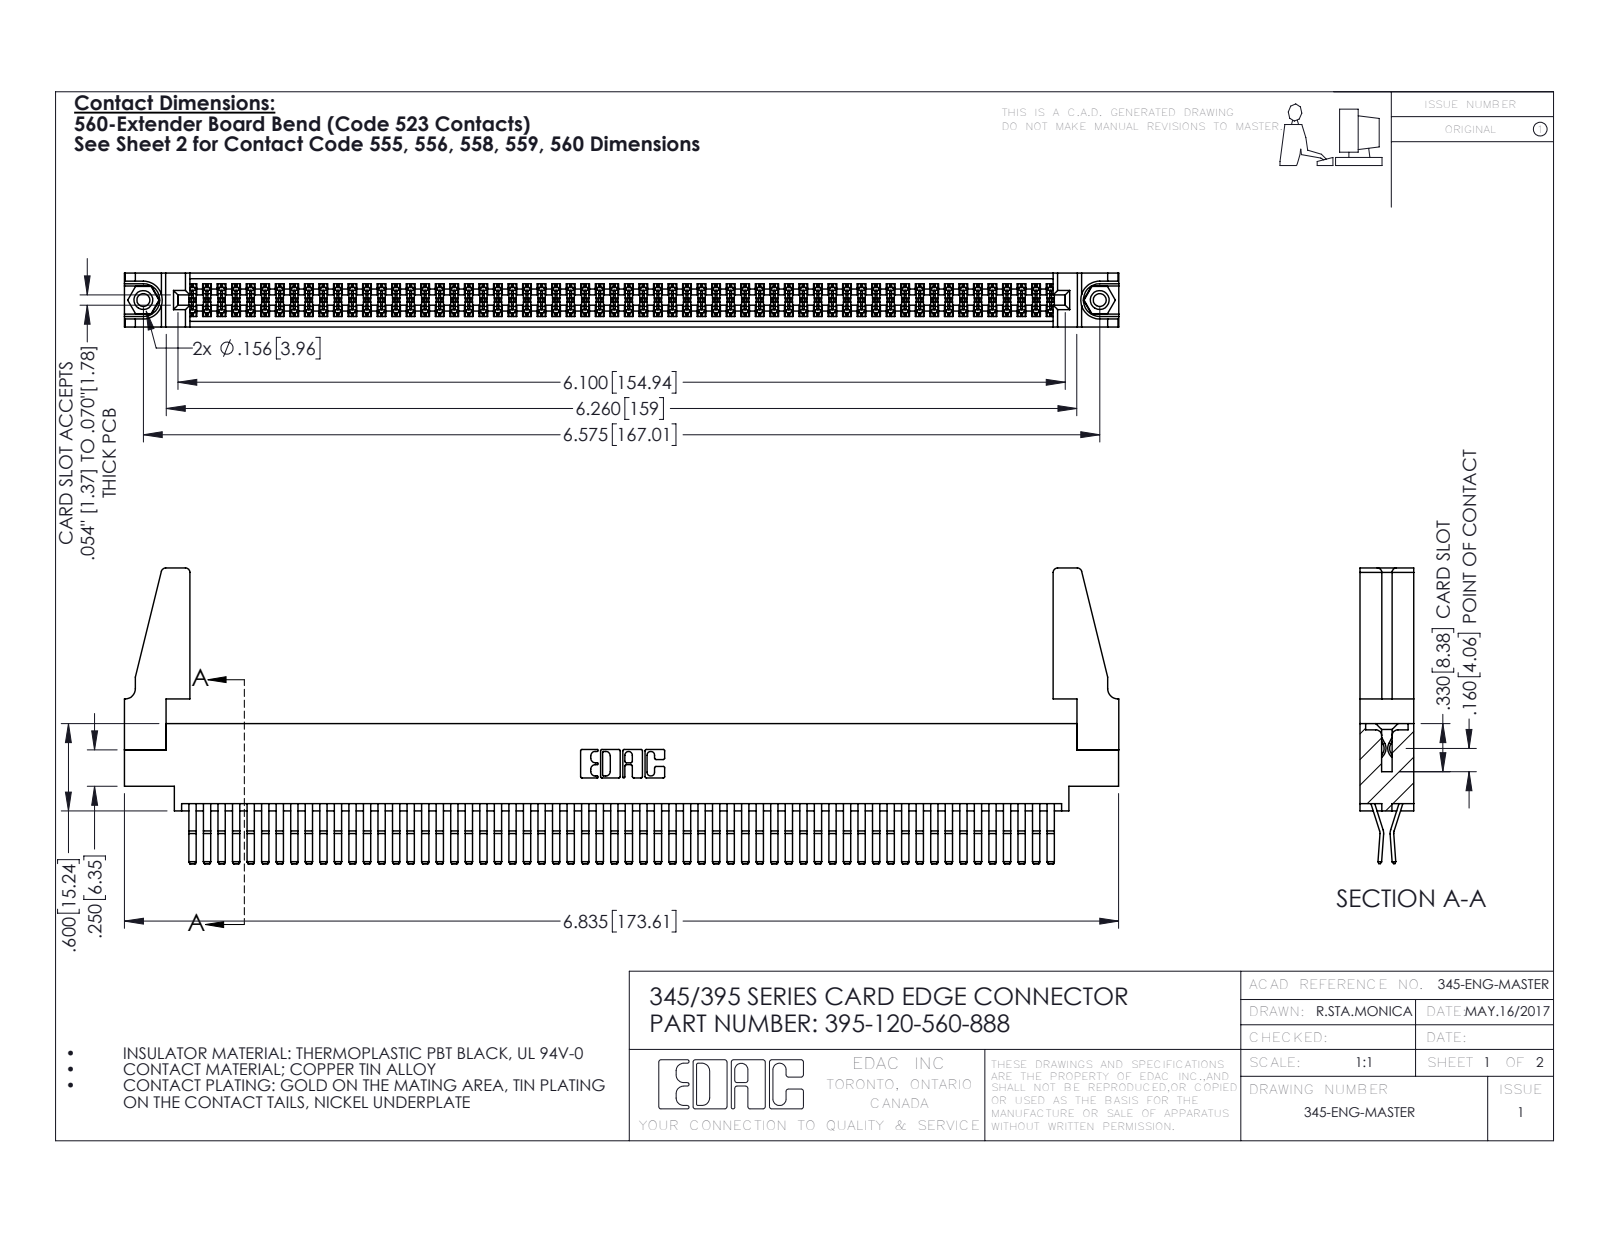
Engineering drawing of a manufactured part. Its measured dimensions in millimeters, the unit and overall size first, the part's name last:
Units: millimetres
Overall size (bounding box): 173.6 × 51.6 × 9.4
Round holes (diameter × count): ⌀2.3 ×2, ⌀3.2 ×2, ⌀4 ×2, ⌀1.6 ×1
Round bosses / shafts (diameter × count): ⌀3.9 ×2
Partial cylindrical surfaces — rounded edges, fillets, slot ends (radius × count): R0.2 ×180, R0.3 ×22, R0.8 ×8, R0.2 ×6, R0.8 ×6, R0.7 ×3, R0.3 ×2, R0.4 ×2
Main face-to-face distances: 1.8, 7.6, 0.6, 9.4, 2.5, 6.9, 5.1, 5.7, 4.4, 3.8
Hole centre spacings: 6.9, 161, 167
Volume: 20 960 mm³ · Surface area: 31 810 mm²
Bodies: 125 solids, 6494 faces (4116 planar, 2362 cylindrical, 16 other)
Part name (STEP PRODUCT): 345-292-001_560 Tail; 345 Part_0.170 Offset - 0.156 Dia-TH; 345-250-001_345-250-001-102; 395-120-560-888 (+1 more)
STEP written by: SolidWorks 2016 (CONFIG_CONTROL_DESIGN)
